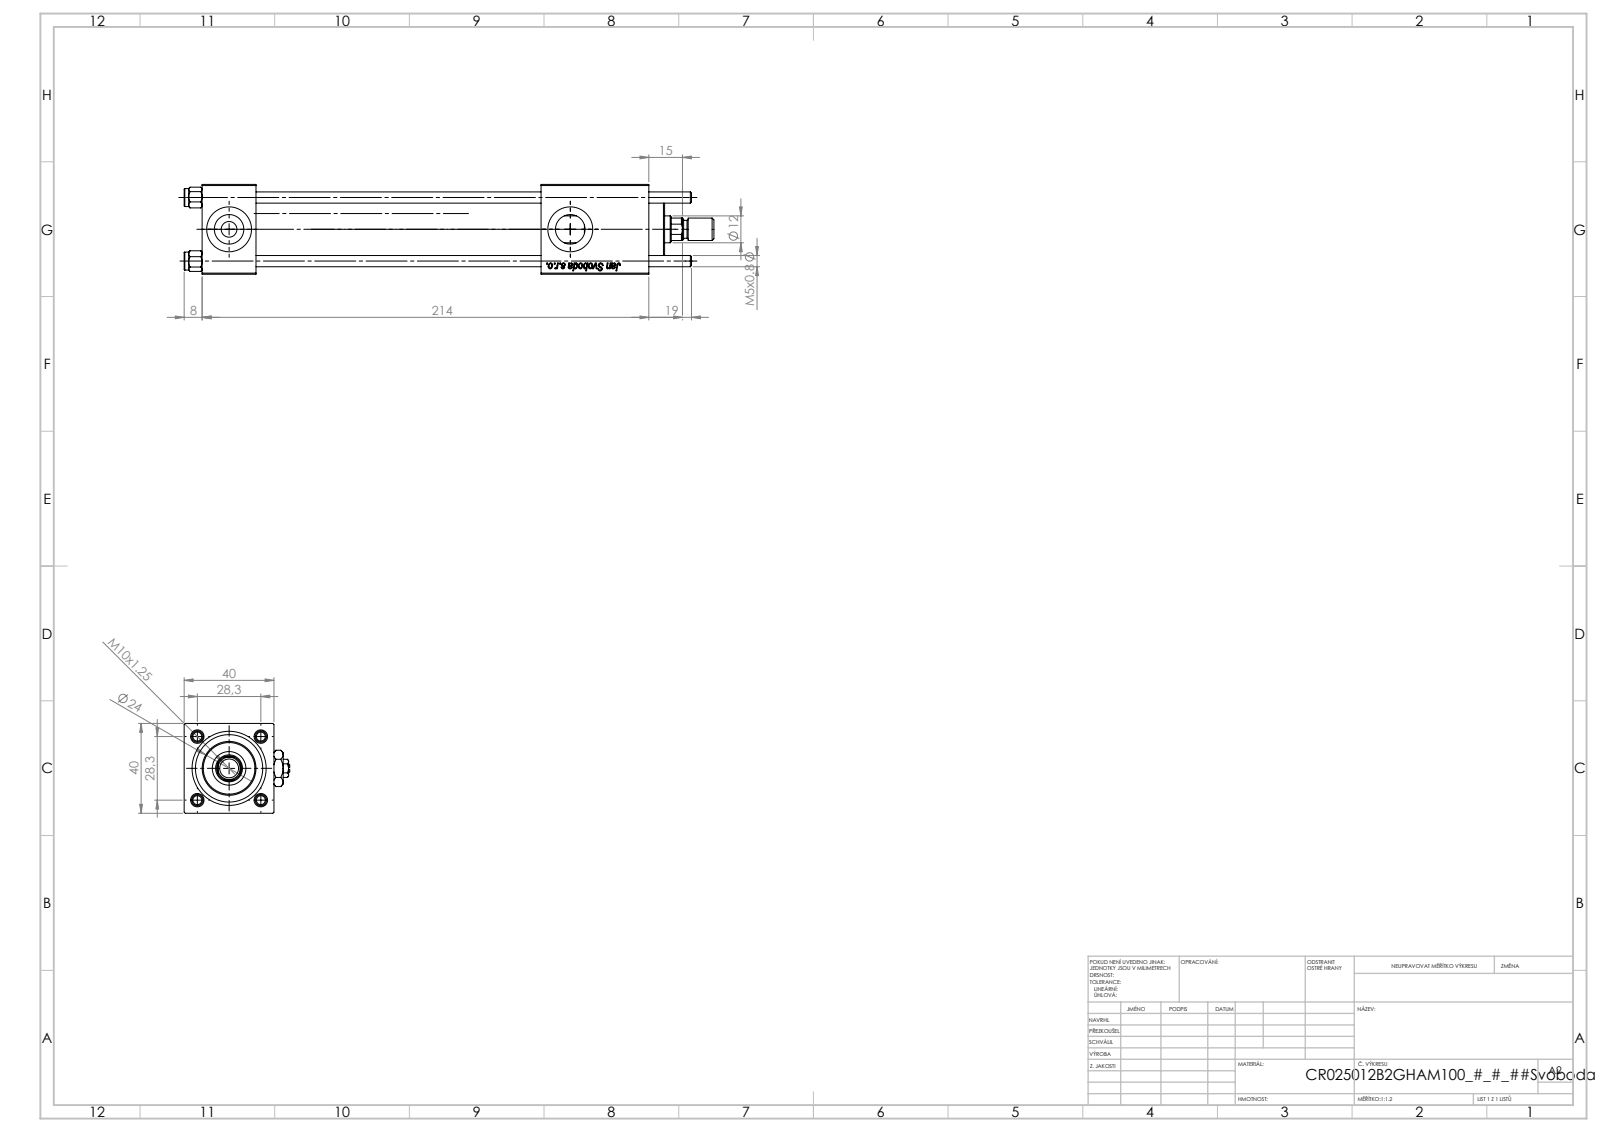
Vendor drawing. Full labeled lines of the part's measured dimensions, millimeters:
Part name (STEP PRODUCT): V215CR_B_TYCINKA; V215_VC_A; Zatka_pro_OIL_PORT; ROD_END_AH (+3 more)
STEP written by: SolidWorks 2019 (CONFIG_CONTROL_DESIGN)
Units: millimetres
Bodies: 13 solids, 1222 faces (456 planar, 90 cylindrical, 676 other)
Overall size (bounding box): 236 × 47 × 40
Volume: 181 605 mm³ · Surface area: 82 371 mm²
Round holes (diameter × count): ⌀5 ×4, ⌀20 ×3, ⌀7 ×2, ⌀13.16 ×2, ⌀6.5 ×1, ⌀12 ×1, ⌀15 ×1, ⌀25 ×1, ⌀30 ×1
Round bosses / shafts (diameter × count): ⌀8 ×5, ⌀31 ×1, ⌀24 ×1, ⌀10 ×1
Partial cylindrical surfaces — rounded edges, fillets, slot ends (radius × count): R5.5 ×1
Main face-to-face distances: 40, 24, 170.3, 146.3, 199, 151, 127, 19.3, 175, 48
Hole centre spacings: 20.01, 28.3, 40.02, 152
